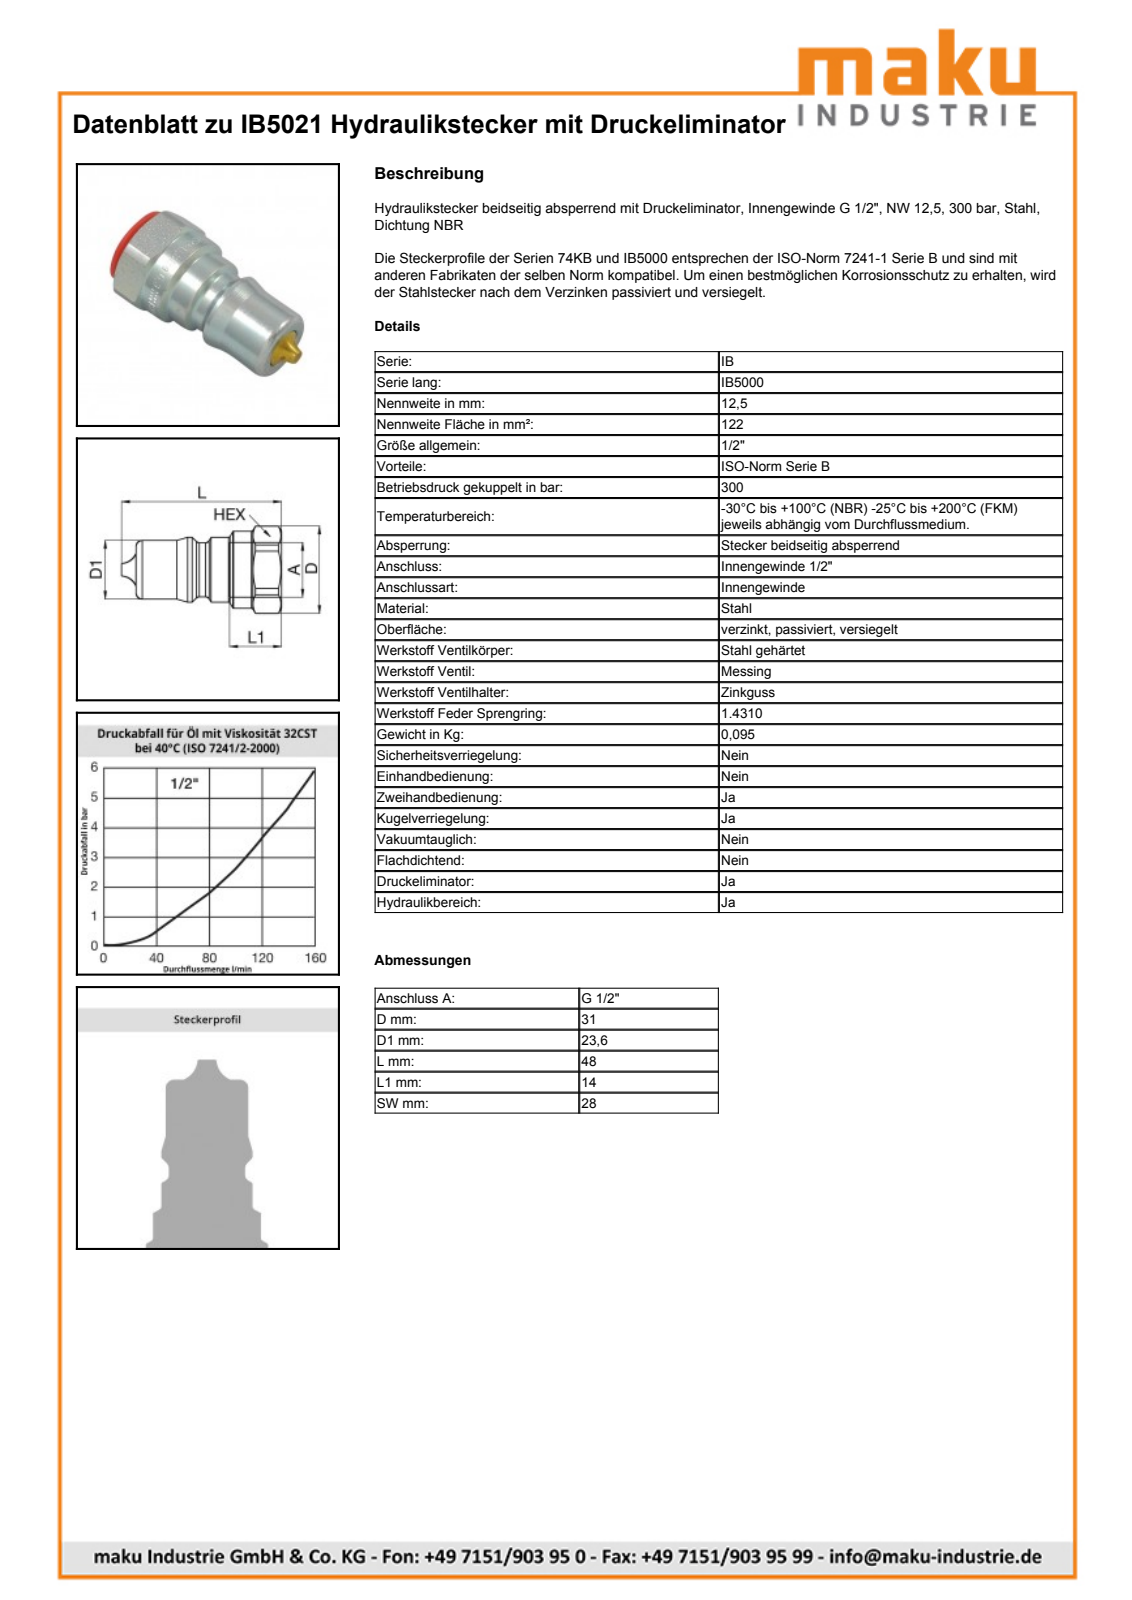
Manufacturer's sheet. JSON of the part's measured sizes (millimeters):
{"part_name": "IB5021", "step_written_by": "SolidWorks 2009 (AUTOMOTIVE_DESIGN)", "units": "millimeters", "bodies": {"solids": 1, "faces": 100, "planar": 13, "cylindrical": 31, "other": 56}, "overall_size": [46.44, 29.5, 27], "volume_mm3": 16593, "surface_area_mm2": 5495, "round_holes": [[1, 2], [2.85, 1], [3.93, 1], [13.2, 1], [18.63, 1]], "round_bosses_or_shafts": [[26.7, 1], [25.8, 1], [23.6, 1], [22.2, 1], [2.75, 1]], "partial_cylinders_radius": [[14.75, 1]], "face_to_face_distances": [27, 16.08, 41.5, 25.42, 46, 29.92, 4.5, 46.05, 29.97, 4.55]}
